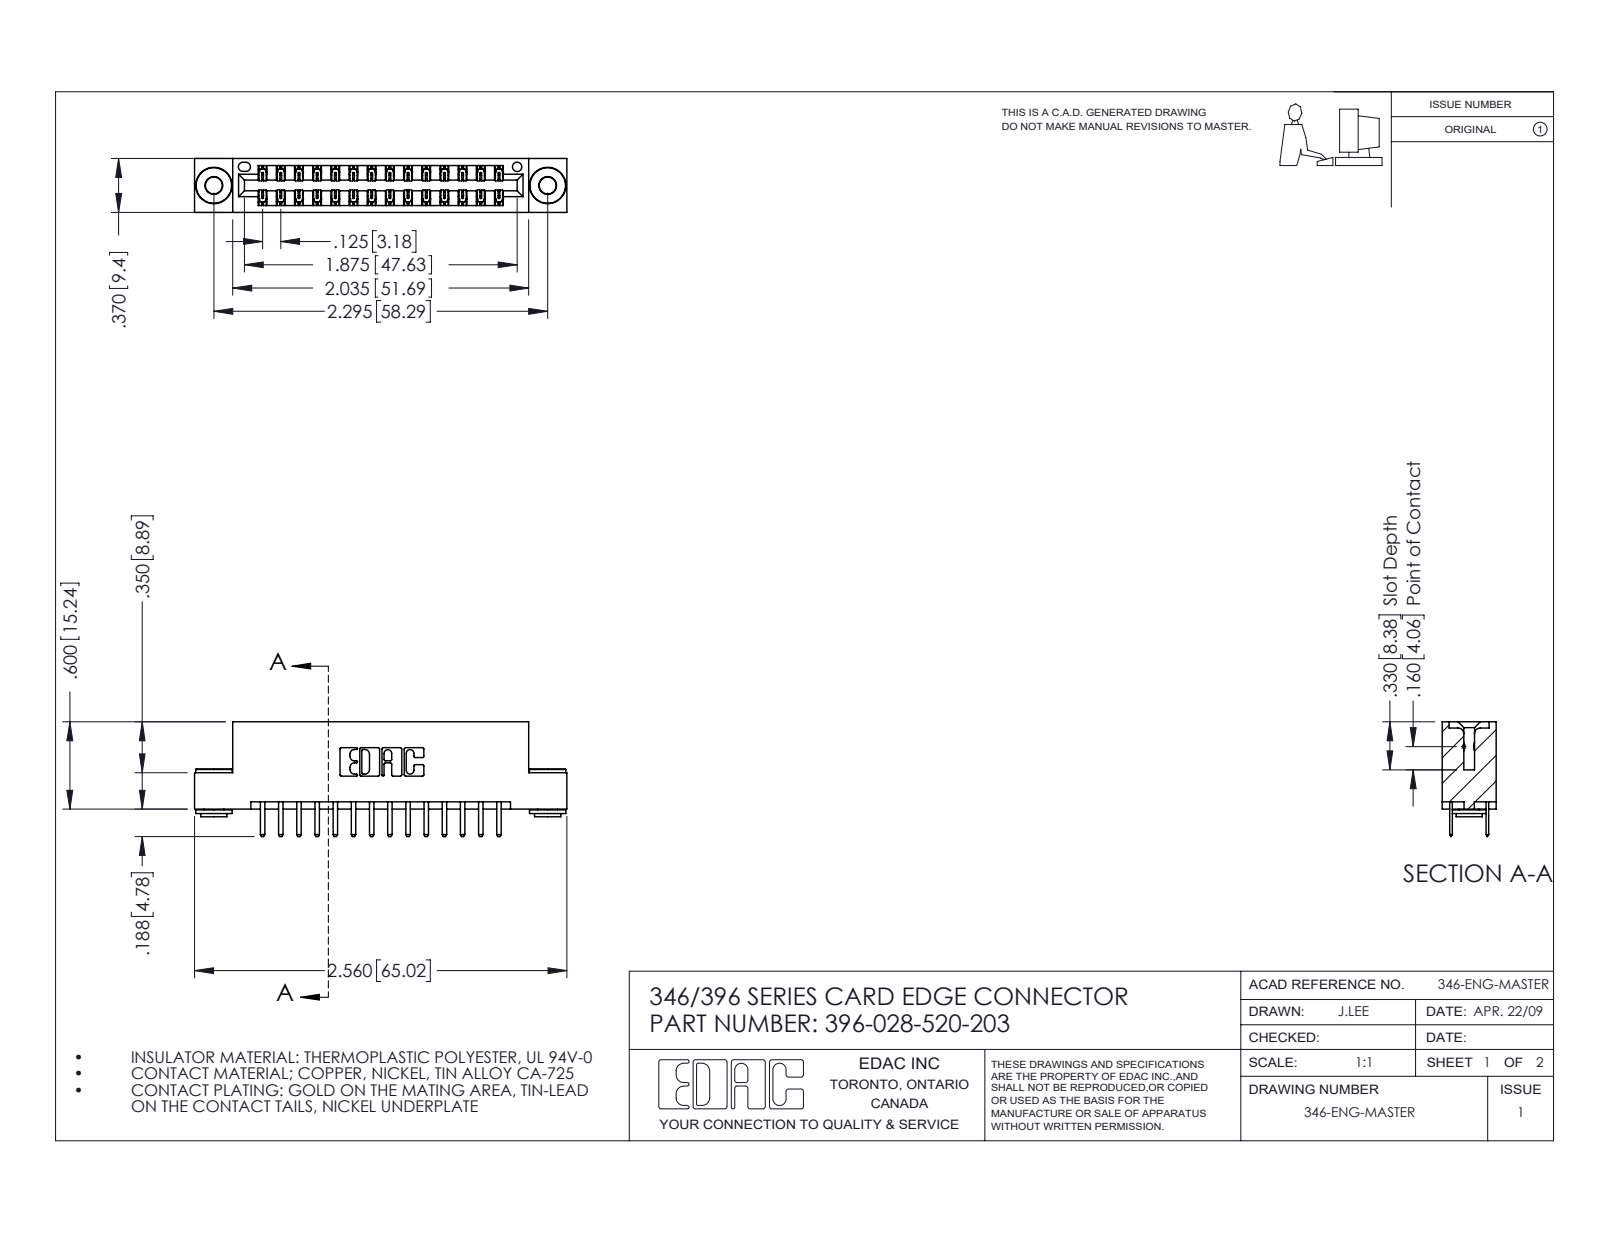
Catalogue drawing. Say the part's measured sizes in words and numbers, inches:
The part is named "345-250-002_345-250-002-102; 396-028-520-203; 345-292-001_345-293-120; 346 Part_Flush Mounting Lugs - 0.156 Dia-TH". Its 3-D file was written by "SolidWorks 2016 (CONFIG_CONTROL_DESIGN)". It is 31 solids with 1728 faces: 1122 planar, 598 cylindrical and 8 other. Overall it measures 2.56 by 0.788 by 0.37 inches. Its volume is 0.374 cubic inches and its surface area 12.67 square inches. Round holes: 2 of diameter 0.116, 2 of diameter 0.156, 1 of diameter 0.064. Round bosses or shafts: 2 of diameter 0.25, 2 of diameter 0.18, 2 of diameter 0.136. Partial cylindrical surfaces (rounded edges, fillets, slot ends): 42 of radius 0.006, 32 of radius 0.01, 22 of radius 0.01, 6 of radius 0.007, 6 of radius 0.031, 3 of radius 0.026, 2 of radius 0.014, 2 of radius 0.022. The main face-to-face distances are 0.25, 0.048, 0.322, 0.37, 0.025, 0.275, 0.072, 0.298, 0.148, 0.222. The hole center spacings are 0.246, 2.089, 2.295.
